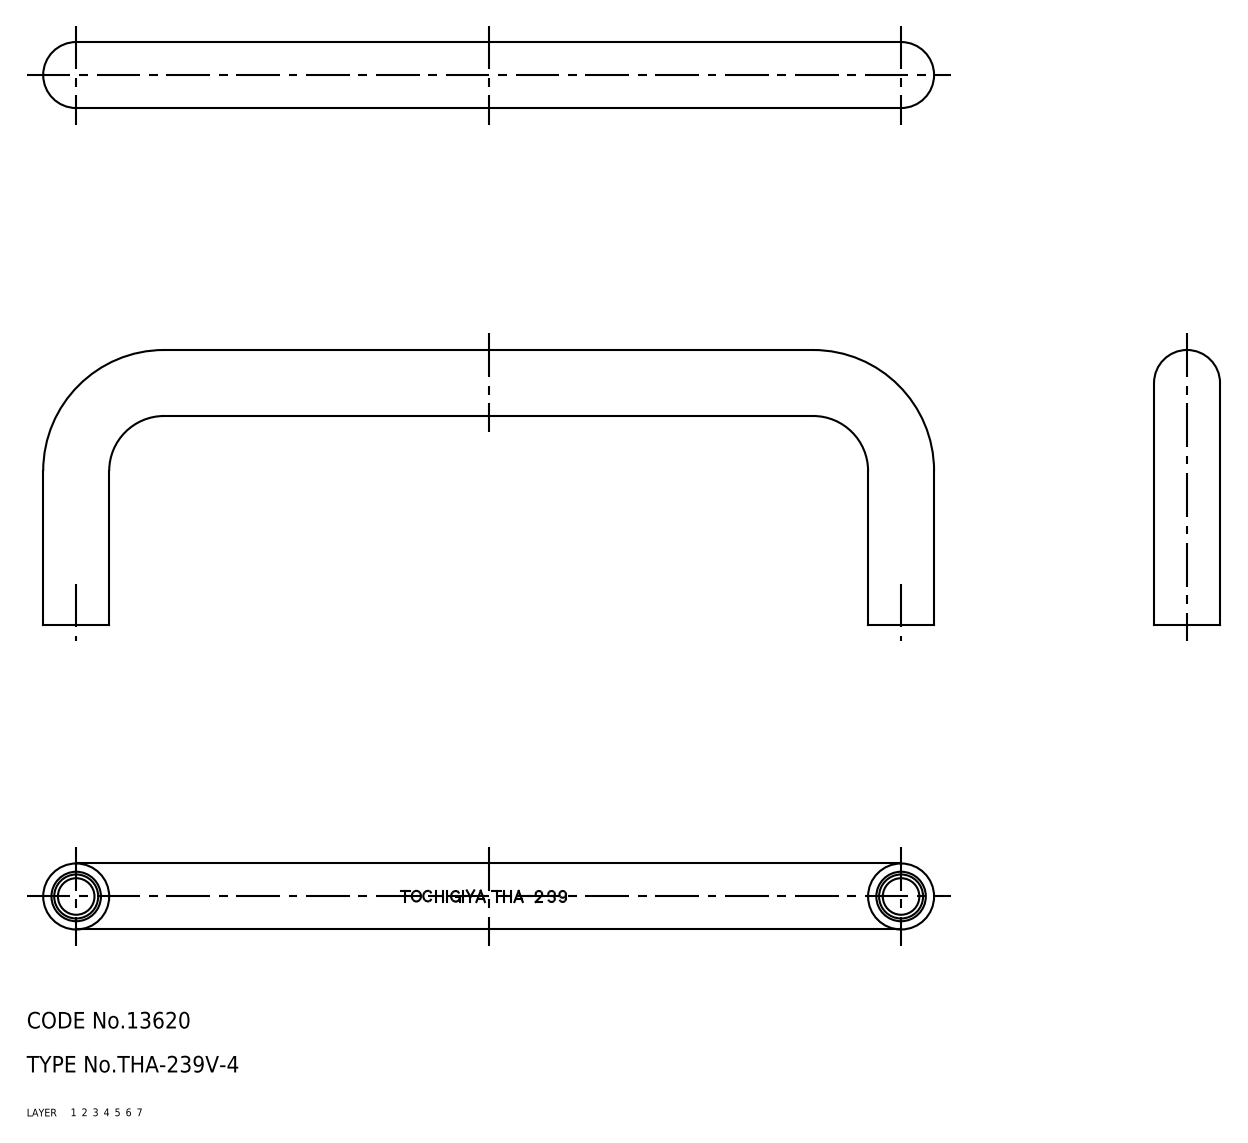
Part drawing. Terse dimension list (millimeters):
name: 67110068
written by: CADfix (AUTOMOTIVE_DESIGN)
unit: mm
bodies: 1 solid, 18 faces (0 planar, 0 cylindrical, 18 other)
size: 162 × 50 × 12
volume: 24 397 mm³; area: 9 193 mm²
